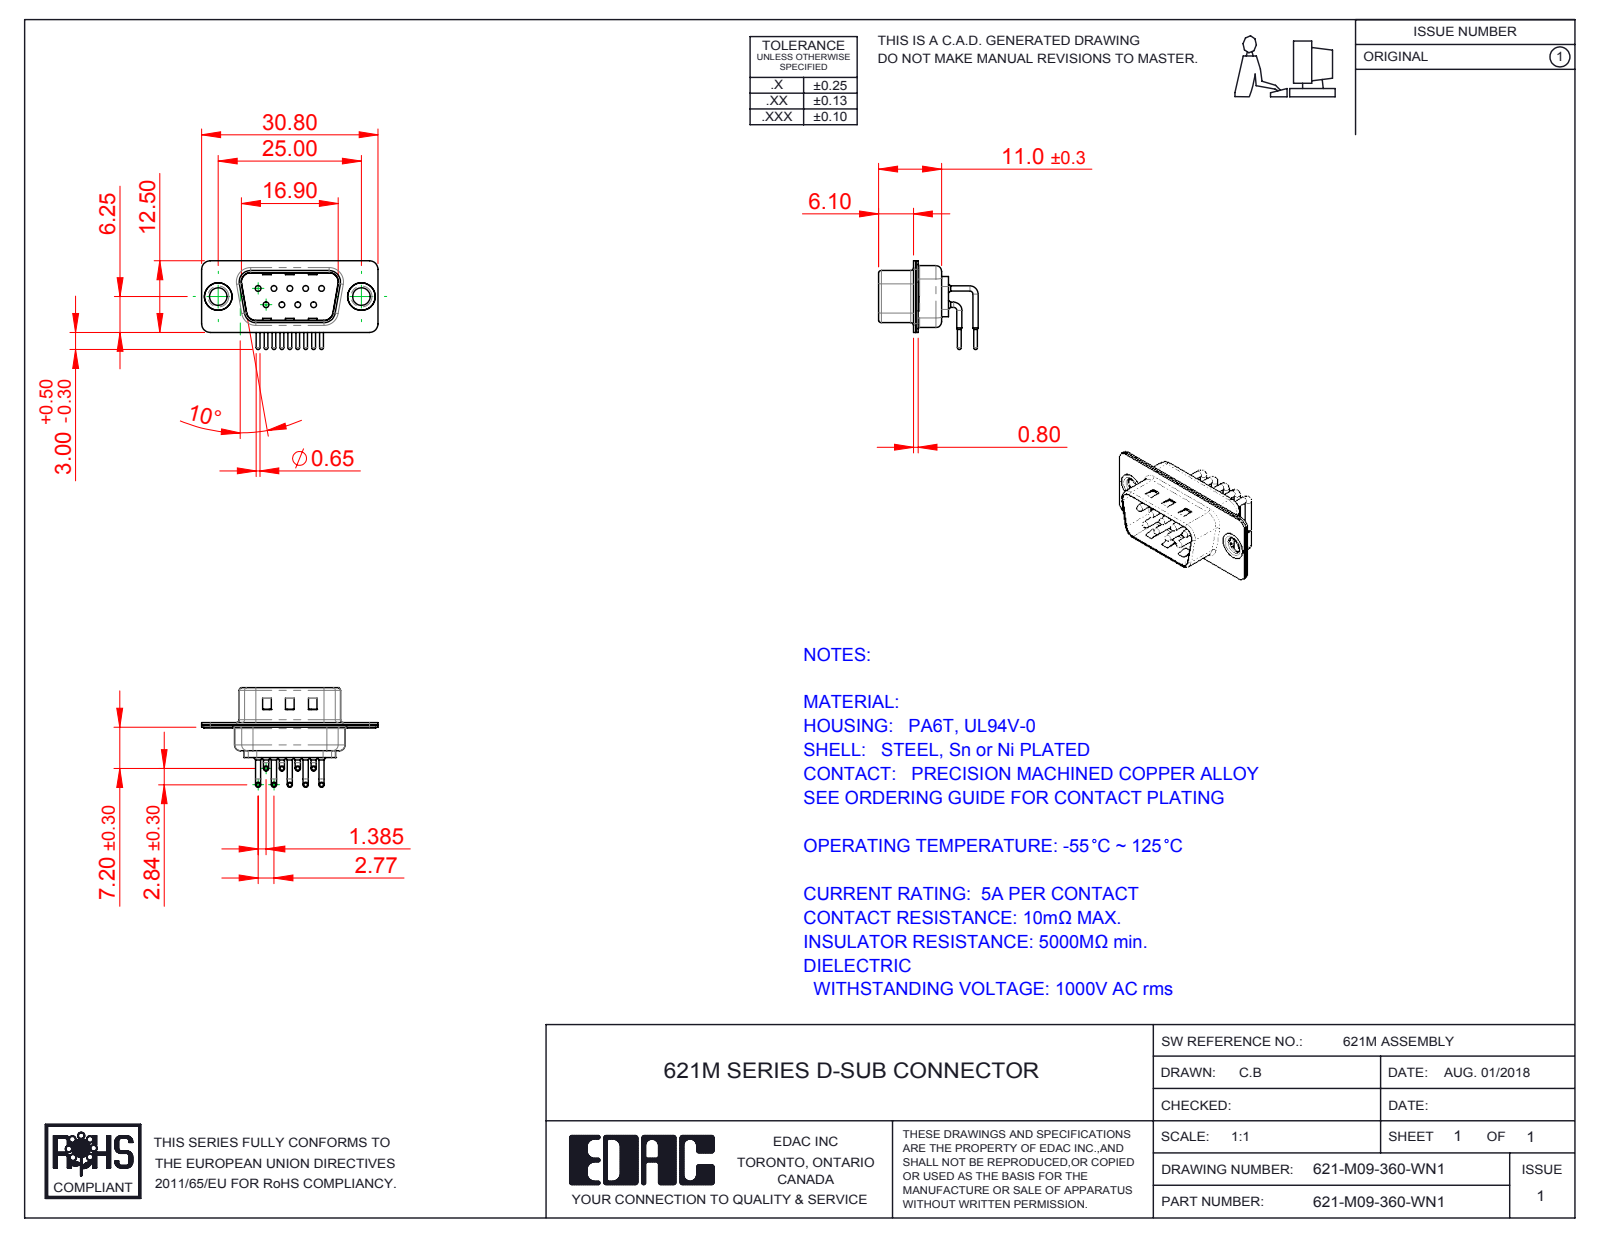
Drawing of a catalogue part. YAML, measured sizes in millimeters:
part_name: "621-M09-360-WN1; 621M Housing_09 Contacts; 621M Shell Front_09 Contacts; 621M Shell Rear_09 Contacts (+3 more)"
step_written_by: "SolidWorks 2016 (CONFIG_CONTROL_DESIGN)"
units: millimeters
bodies: {solids: 14, faces: 1268, planar: 683, cylindrical: 437, other: 148}
overall_size: [30.8, 17.39, 15.49]
volume: 1289
surface_area: 3701
round_holes:
  - {diameter: 1, count: 9}
  - {diameter: 1.7, count: 9}
  - {diameter: 2, count: 9}
  - {diameter: 3.05, count: 2}
  - {diameter: 4, count: 2}
  - {diameter: 4.8, count: 2}
round_bosses_or_shafts:
  - {diameter: 0.9, count: 18}
  - {diameter: 1.5, count: 9}
  - {diameter: 0.65, count: 9}
  - {diameter: 5, count: 2}
  - {diameter: 4.9, count: 2}
  - {diameter: 3.55, count: 2}
partial_cylinders:
  - {radius: 1.5, count: 16}
  - {radius: 2, count: 12}
  - {radius: 1.01, count: 9}
  - {radius: 0.5, count: 8}
  - {radius: 1.6, count: 8}
  - {radius: 0.25, count: 4}
  - {radius: 0.6, count: 4}
  - {radius: 0.65, count: 4}
face_to_face_distances: [0.4, 0.85, 0.8, 9.55, 1.25, 10.4, 8.7, 0.35, 6.1, 5.7]
hole_center_spacings: [3.16, 2.77, 5.54, 5.03, 5.04, 8.31, 7.1, 7.48]
